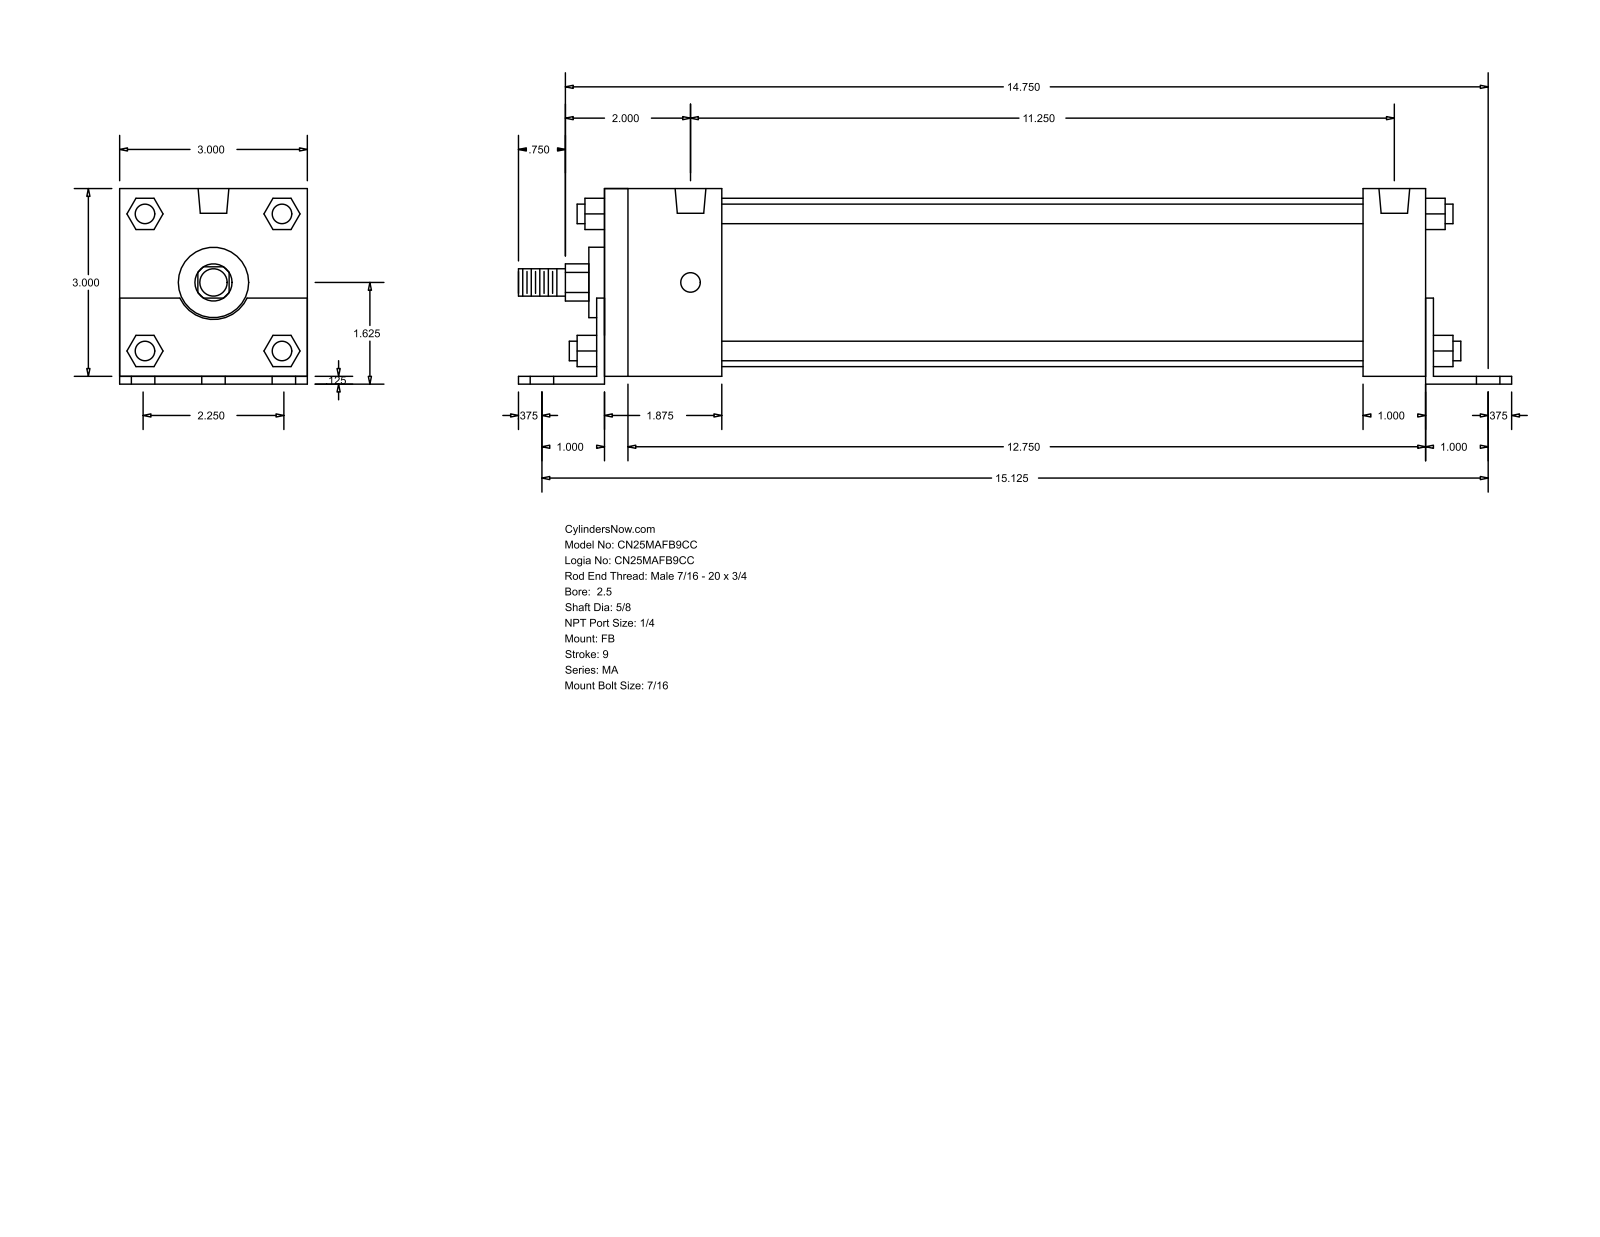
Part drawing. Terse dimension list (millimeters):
name: MA_FB__0250_0.625
written by: GSSL Pune (CONFIG_CONTROL_DESIGN)
unit: mm
bodies: 0 solids, 140 faces (105 planar, 35 cylindrical, 0 other)
size: 403.23 × 79.38 × 76.2
holes: 6× ⌀11.11, 4× ⌀7.94, 2× ⌀12.49
bosses: 4× ⌀7.94, 1× ⌀68.33, 1× ⌀28.57, 1× ⌀15.88, 1× ⌀11.11
rounds: 1× R7.54, 1× R15.05
face distances: 76.2, 3.17, 79.37, 3.18, 336.55, 333.37, 28.58, 47.62, 25.4, 339.73
hole spacings: 28.57, 385.24, 384.18, 47.62, 57.14, 66.75, 285.75, 325.11
